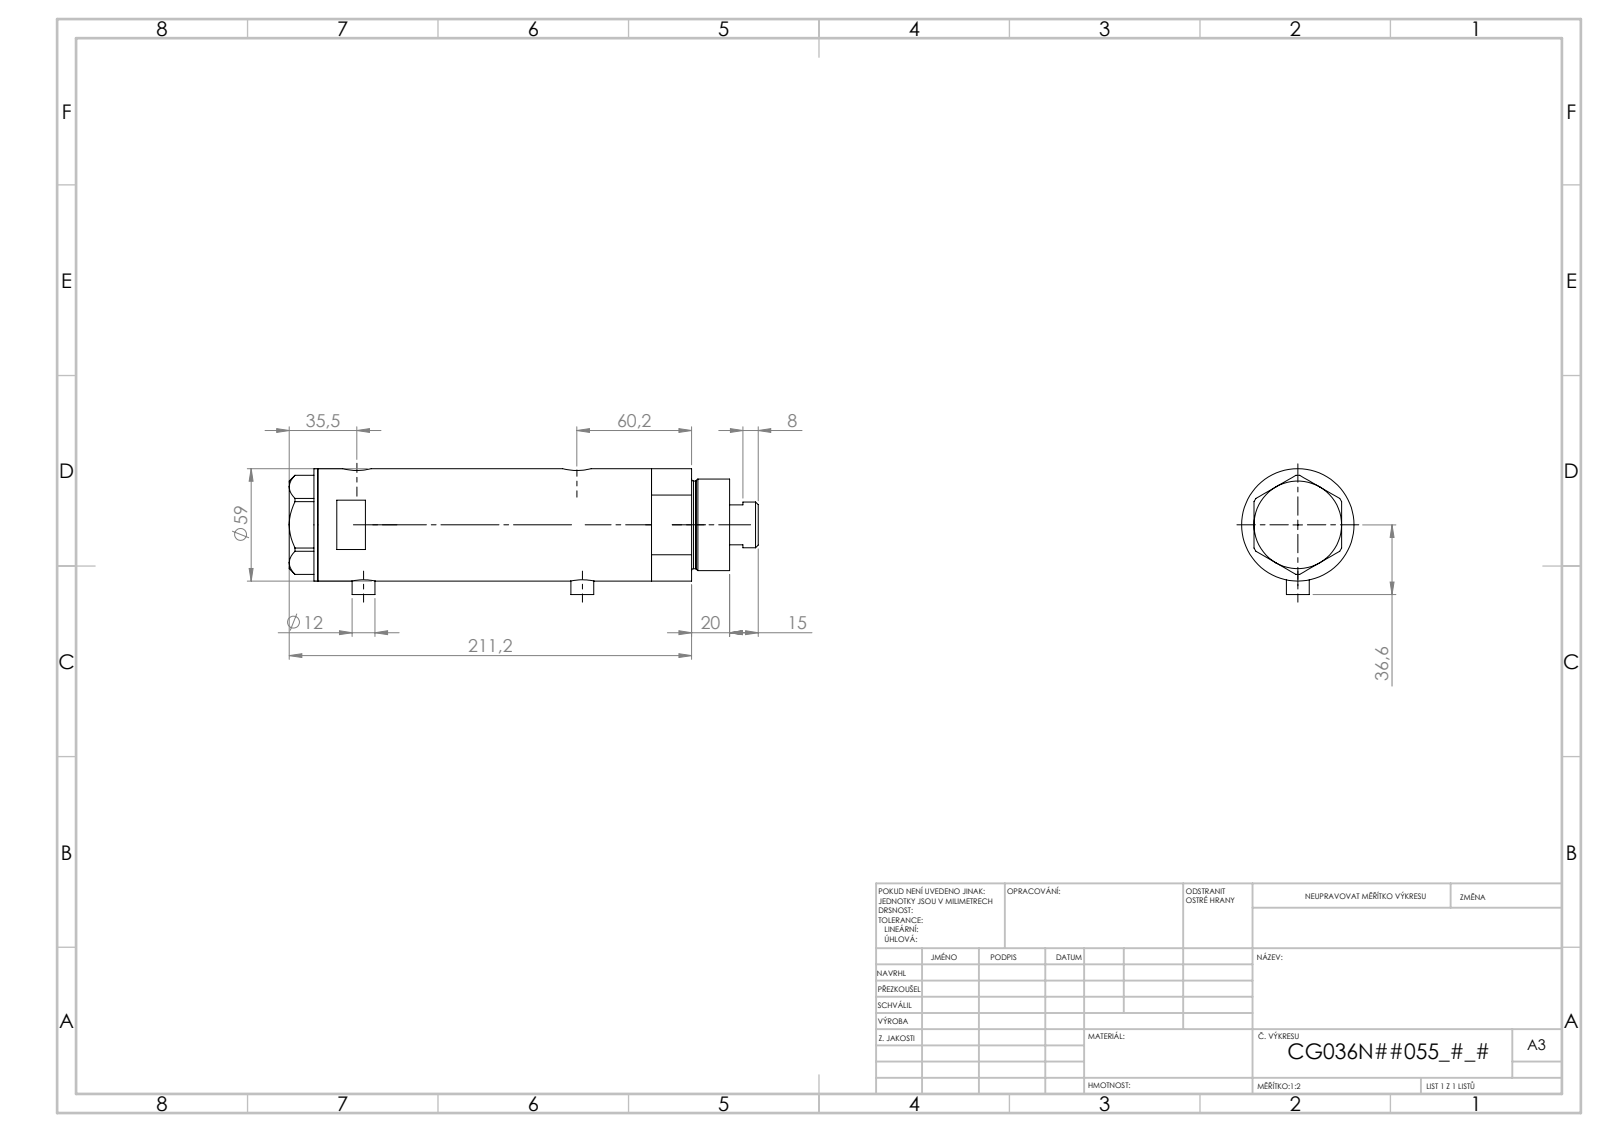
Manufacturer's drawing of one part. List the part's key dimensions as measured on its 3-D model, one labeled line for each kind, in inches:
Part name (STEP PRODUCT): V270CG_FRONT; V270CG_MIDDLE; V270CG_BACK; V270CG_VC
STEP written by: SolidWorks 2019 (CONFIG_CONTROL_DESIGN)
Units: inches
Bodies: 4 solids, 126 faces (53 planar, 53 cylindrical, 20 other)
Overall size (bounding box): 8.599 × 2.366 × 2.323
Volume: 30.06 in³ · Surface area: 159.1 in²
Round holes (diameter × count): ⌀0.197 ×2, ⌀0.383 ×2, ⌀0.492 ×2, ⌀0.591 ×2, ⌀0.335 ×1, ⌀0.984 ×1, ⌀1.043 ×1, ⌀1.417 ×1, ⌀1.575 ×1, ⌀2.047 ×1
Round bosses / shafts (diameter × count): ⌀0.472 ×2, ⌀2.323 ×1, ⌀1.89 ×1, ⌀1.811 ×1, ⌀0.945 ×1
Main face-to-face distances: 4.423, 0.925, 3.498, 0.591, 1.516, 5.013, 8.009, 7.418, 6.493, 2.995
Hole centre spacings: 0.114, 0.138, 3.431, 3.545, 3.569, 3.683, 0.114, 0.115
